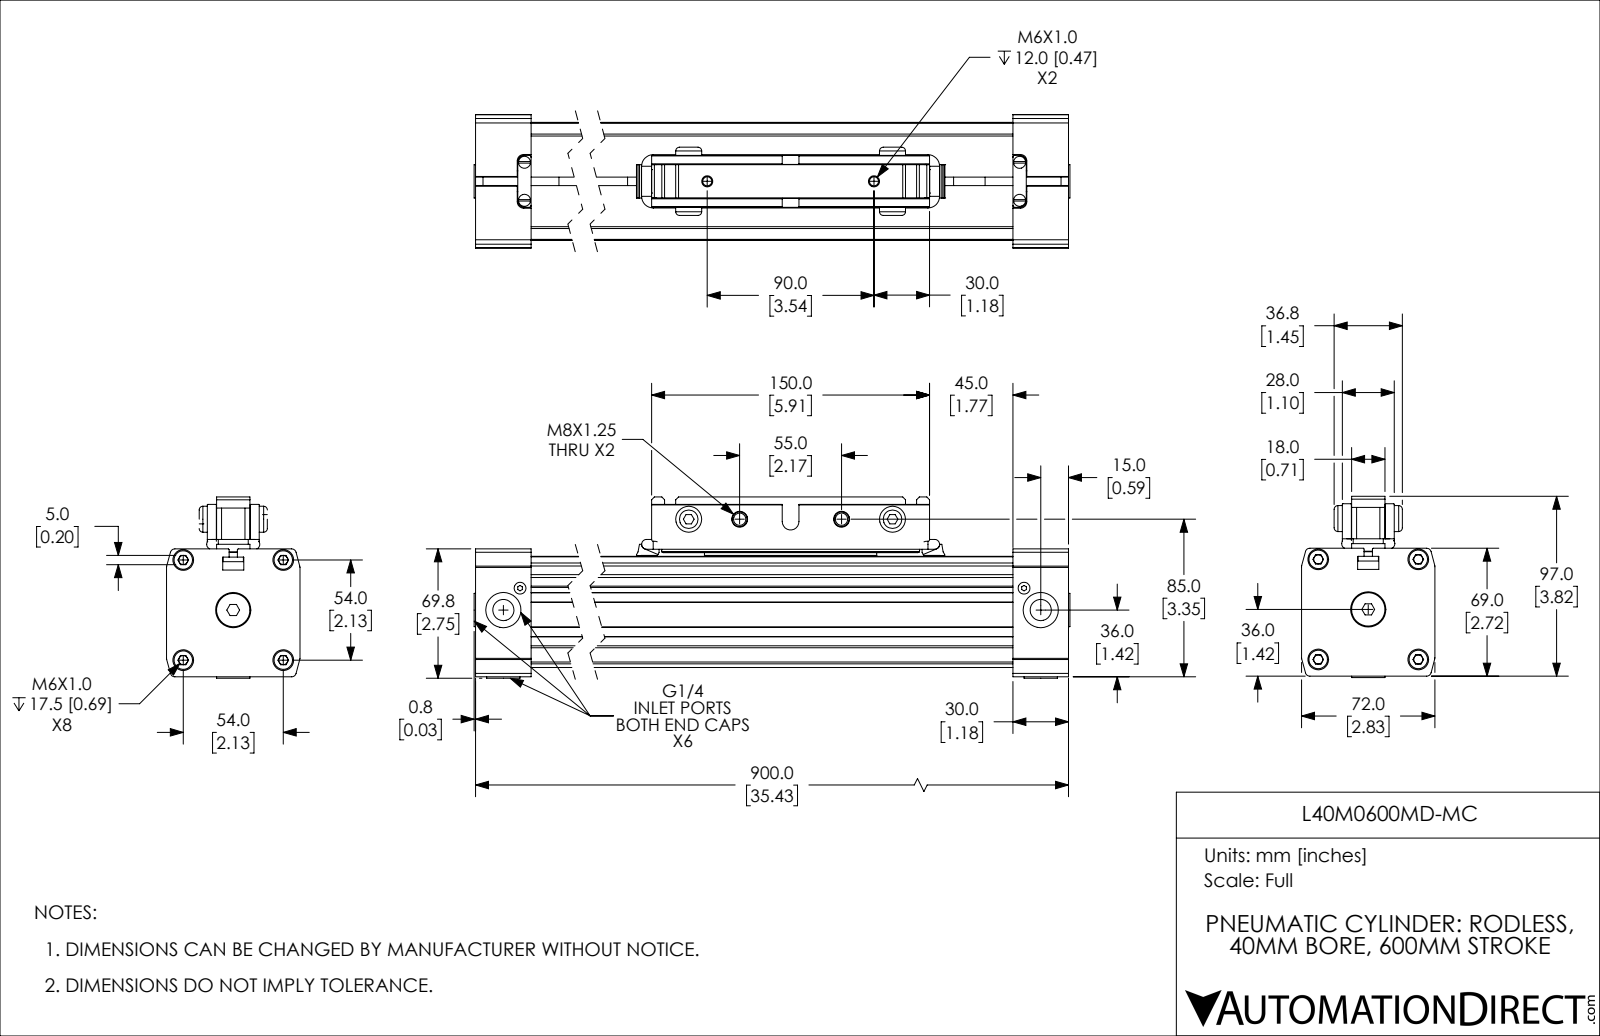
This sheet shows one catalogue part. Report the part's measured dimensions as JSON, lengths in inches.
{"part_name": "L40M0600MD-MC_PISTON; L40M0600MD-MC; L40M0600MD-MC_BODY", "step_written_by": "SolidWorks 2019 (CONFIG_CONTROL_DESIGN)", "units": "inches", "bodies": {"solids": 13, "faces": 821, "planar": 451, "cylindrical": 278, "other": 92}, "overall_size": [35.495, 3.85, 2.835], "volume_in3": 147.2, "surface_area_in2": 788.2, "round_holes": [[0.194, 6], [0.451, 5], [0.748, 5], [0.256, 4], [0.262, 4], [0.339, 4], [0.441, 4], [0.252, 2], [1.583, 1]], "round_bosses_or_shafts": [[0.394, 4], [0.21, 4], [0.709, 3], [0.437, 3], [0.551, 2], [0.518, 2], [1.575, 1], [0.518, 1]], "partial_cylinders_radius": [[0.039, 30], [0.079, 10], [0.012, 8], [0.098, 8], [0.138, 8], [0.157, 4], [0.006, 2], [0.008, 2]], "face_to_face_distances": [2.362, 0.201, 2.504, 2.303, 0.732, 0.701, 1.45, 1.181, 0.031, 0.274], "hole_center_spacings": [0.604, 1.503, 2.126, 33.806, 0.584, 0.807, 1.083, 1.428]}
